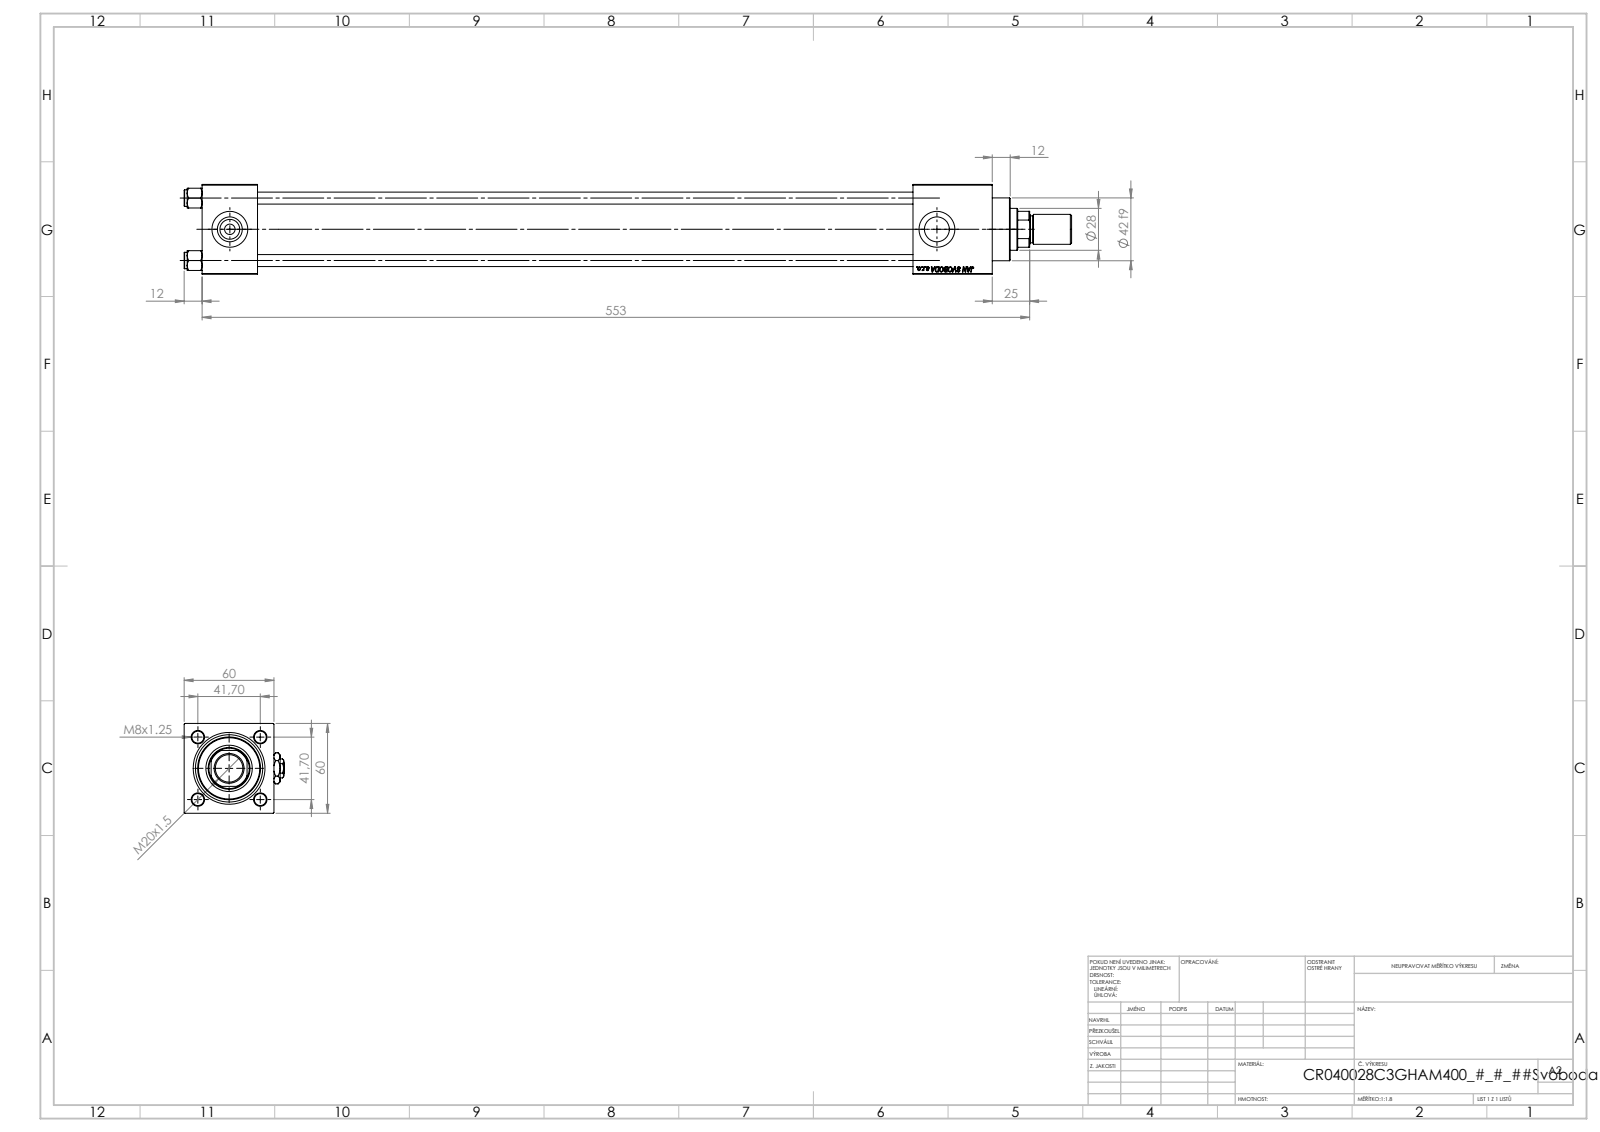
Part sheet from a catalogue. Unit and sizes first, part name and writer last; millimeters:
Units: millimetres
Overall size (bounding box): 593 × 67 × 60
Round holes (diameter × count): ⌀8 ×4, ⌀7 ×2, ⌀16.66 ×2, ⌀24 ×2, ⌀18.5 ×1, ⌀28 ×1, ⌀31 ×1, ⌀40 ×1, ⌀45 ×1
Round bosses / shafts (diameter × count): ⌀11 ×4, ⌀46 ×1, ⌀42 ×1, ⌀20 ×1, ⌀18 ×1
Partial cylindrical surfaces — rounded edges, fillets, slot ends (radius × count): R13.5 ×1
Main face-to-face distances: 60, 37, 475, 438, 53, 499.3, 462.3, 24.3, 528, 491
Hole centre spacings: 29.49, 41.7, 58.97, 472.5
Volume: 893 981 mm³ · Surface area: 291 079 mm²
Bodies: 14 solids, 1264 faces (578 planar, 102 cylindrical, 584 other)
Part name (STEP PRODUCT): NUT_M5_C; ROD_END_AH; V215_VC_A; V215CR_C_Body (+3 more)
STEP written by: SolidWorks 2019 (CONFIG_CONTROL_DESIGN)
